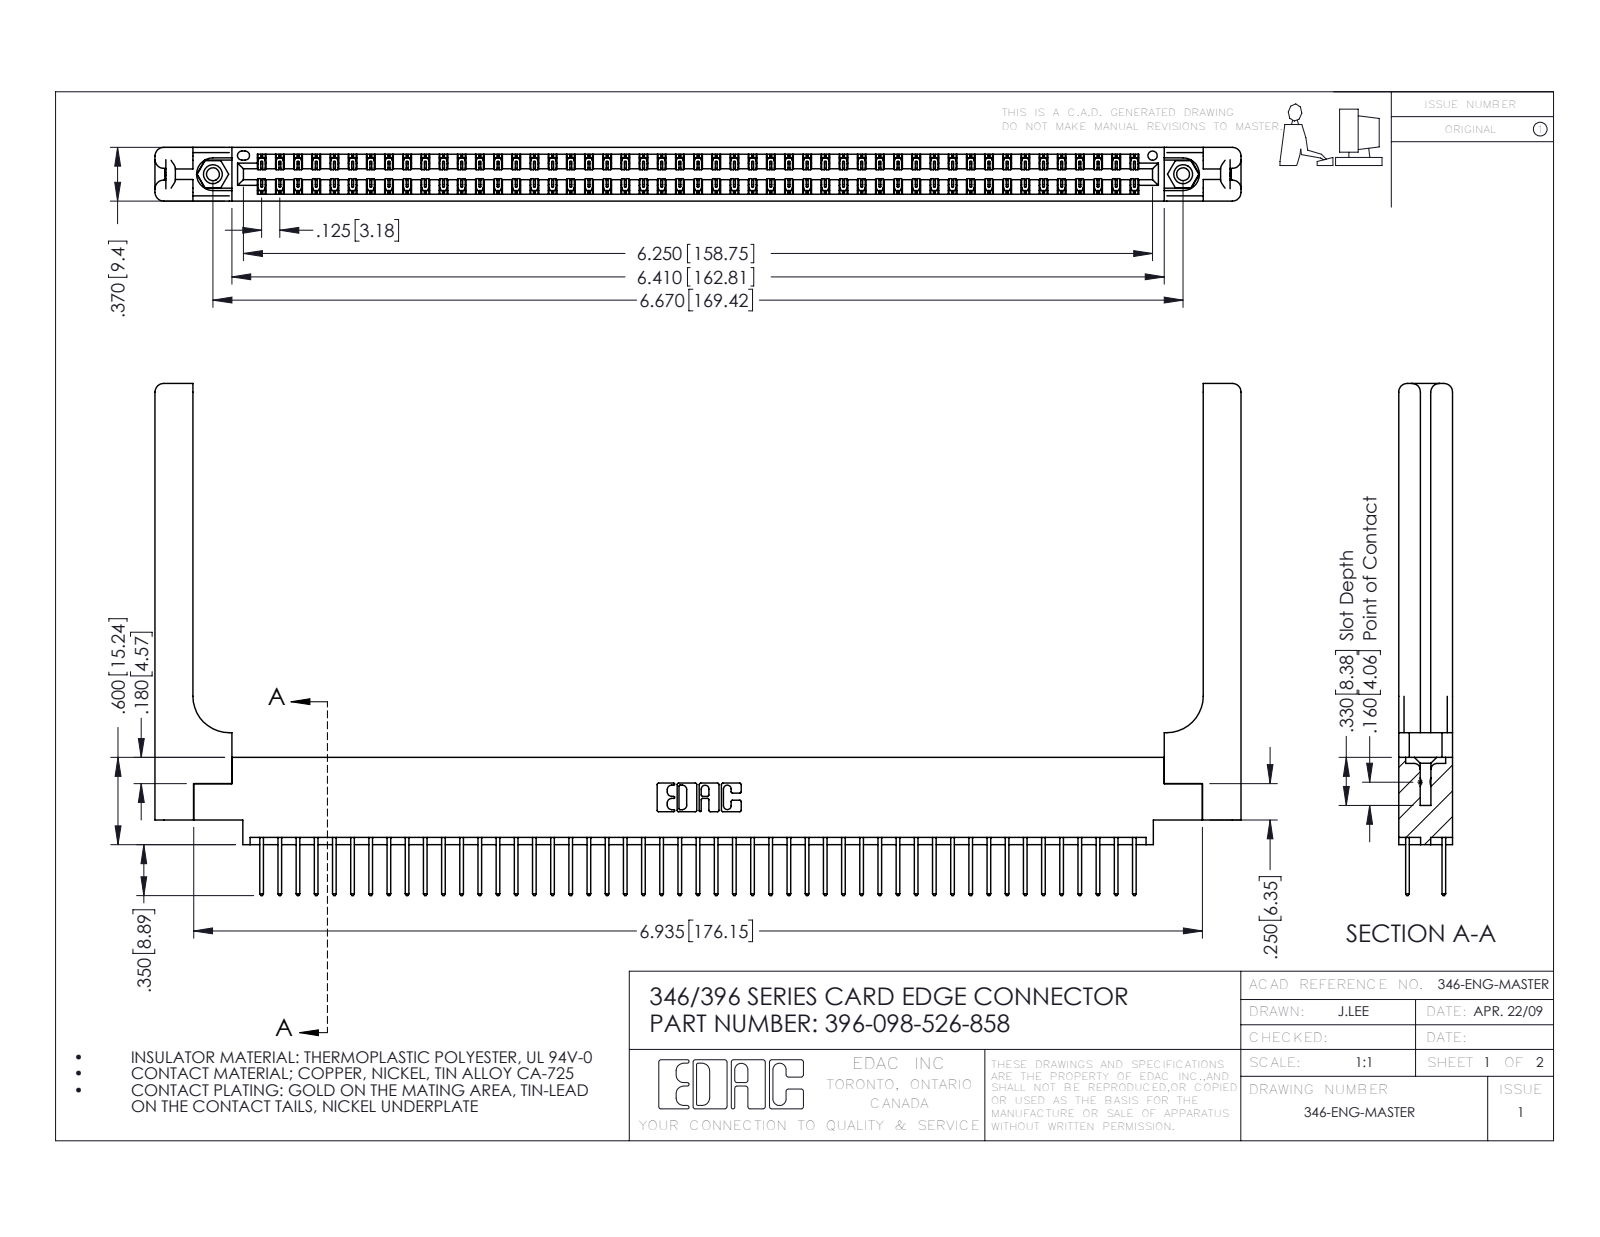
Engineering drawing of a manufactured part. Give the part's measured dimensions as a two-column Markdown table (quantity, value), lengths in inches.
| quantity | value |
| --- | --- |
| part name | 345-292-001_345-293-126; 396-098-526-858; 345-250-001_345-250-001-102; 346-220-058_345-220-058 (+1 more) |
| STEP written by | SolidWorks 2016 (CONFIG_CONTROL_DESIGN) |
| units | inches |
| bodies | 103 solids, 5478 faces (3658 planar, 1760 cylindrical, 60 other) |
| overall size | 7.466 × 3.52 × 0.37 |
| volume | 1.589 in³ |
| surface area | 48.8 in² |
| round holes (diameter × count) | 0.089 × 2, 0.125 × 2, 0.156 × 2, 0.064 × 1 |
| round bosses / shafts (diameter × count) | 0.155 × 2 |
| partial cylindrical surfaces (radius × count) | 0.006 × 147, 0.01 × 98, 0.01 × 22, 0.06 × 16, 0.007 × 6, 0.031 × 6, 0.026 × 3, 0.014 × 2 |
| main face-to-face distances | 0.048, 0.322, 0.37, 0.072, 0.25, 0.025, 0.298, 0.148, 0.15, 0.275 |
| hole center spacings | 0.246, 6.461, 6.67 |
